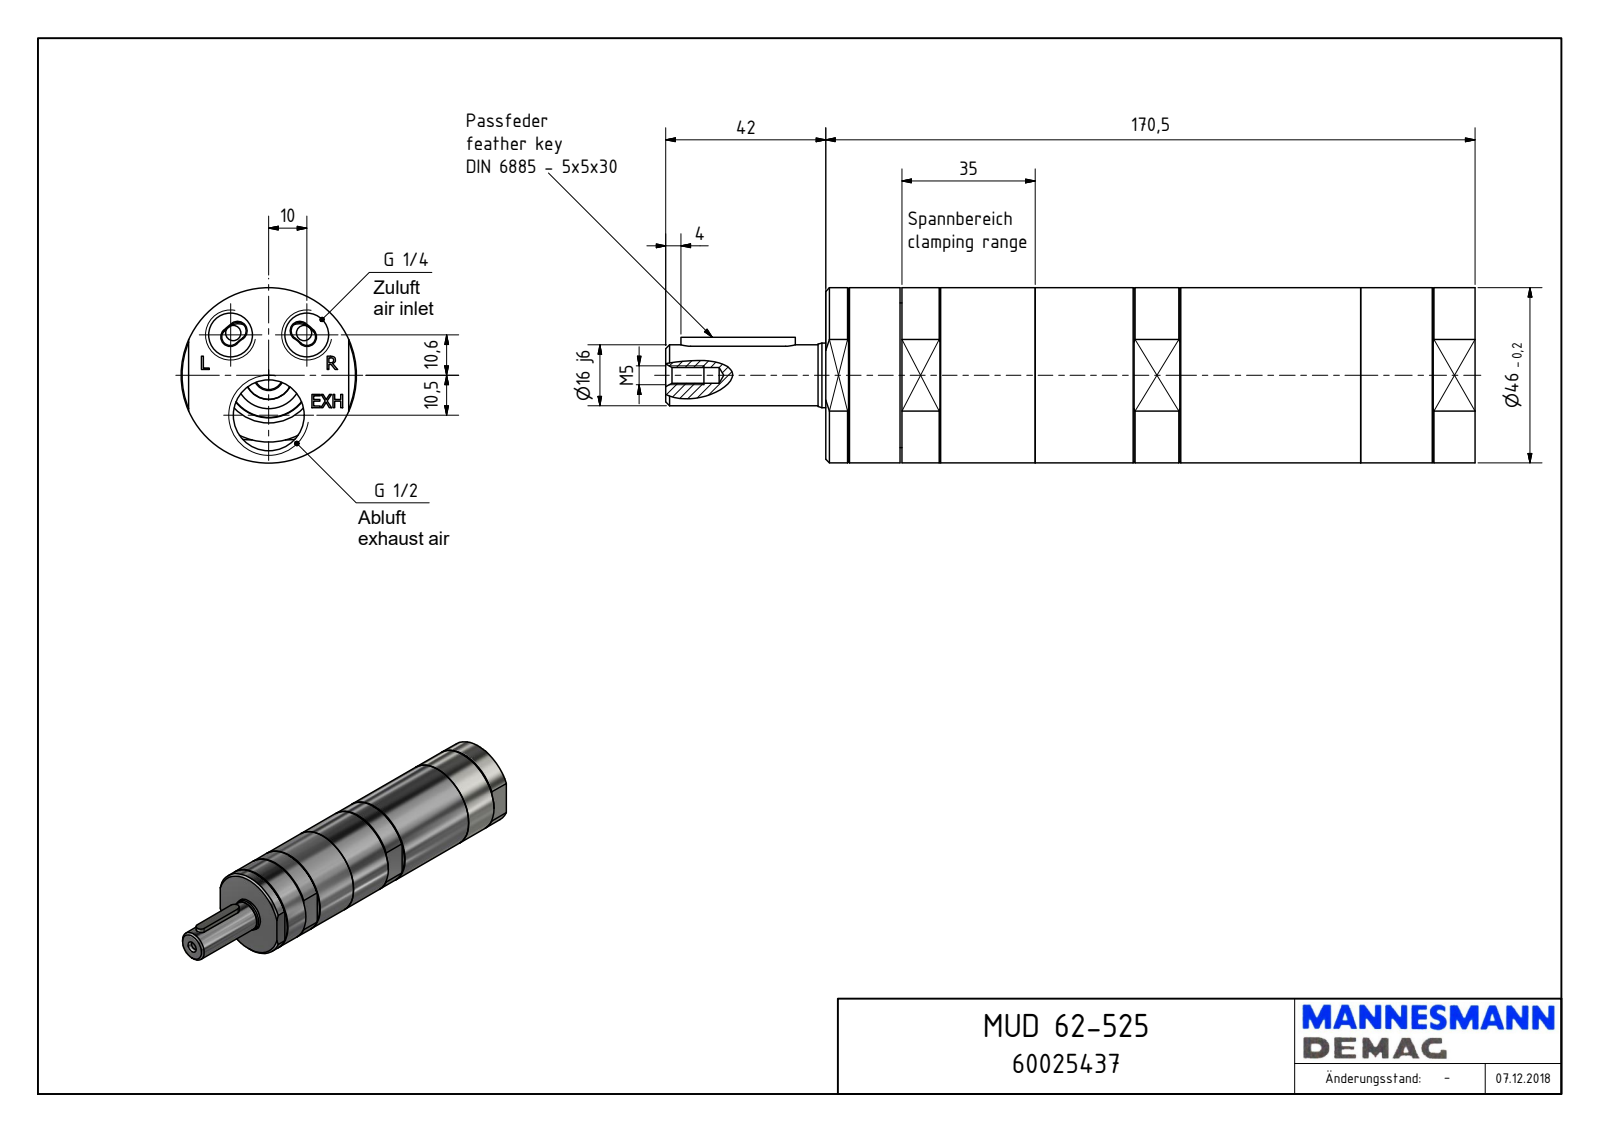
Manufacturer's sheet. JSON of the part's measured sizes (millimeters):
{"part_name": "MUD 62-525_60025437", "step_written_by": "Autodesk Inventor 2018 (AUTOMOTIVE_DESIGN)", "units": "millimeters", "bodies": {"solids": 1, "faces": 175, "planar": 100, "cylindrical": 32, "other": 43}, "overall_size": [212.5, 46, 46], "volume_mm3": 284861, "surface_area_mm2": 35043, "round_holes": [[11.45, 2], [4.13, 1], [17.5, 1], [18.63, 1], [21.5, 1], [23, 1], [38, 1], [38.38, 1]], "round_bosses_or_shafts": [[46, 1], [19.56, 1], [16.95, 1], [16, 1]], "partial_cylinders_radius": [[2.5, 2], [5, 2]], "face_to_face_distances": [170.5, 42, 20, 150.5, 19.5, 0.5, 151, 163.61, 144.11, 143.61], "hole_center_spacings": [14.57, 23.35, 10.5, 20]}
